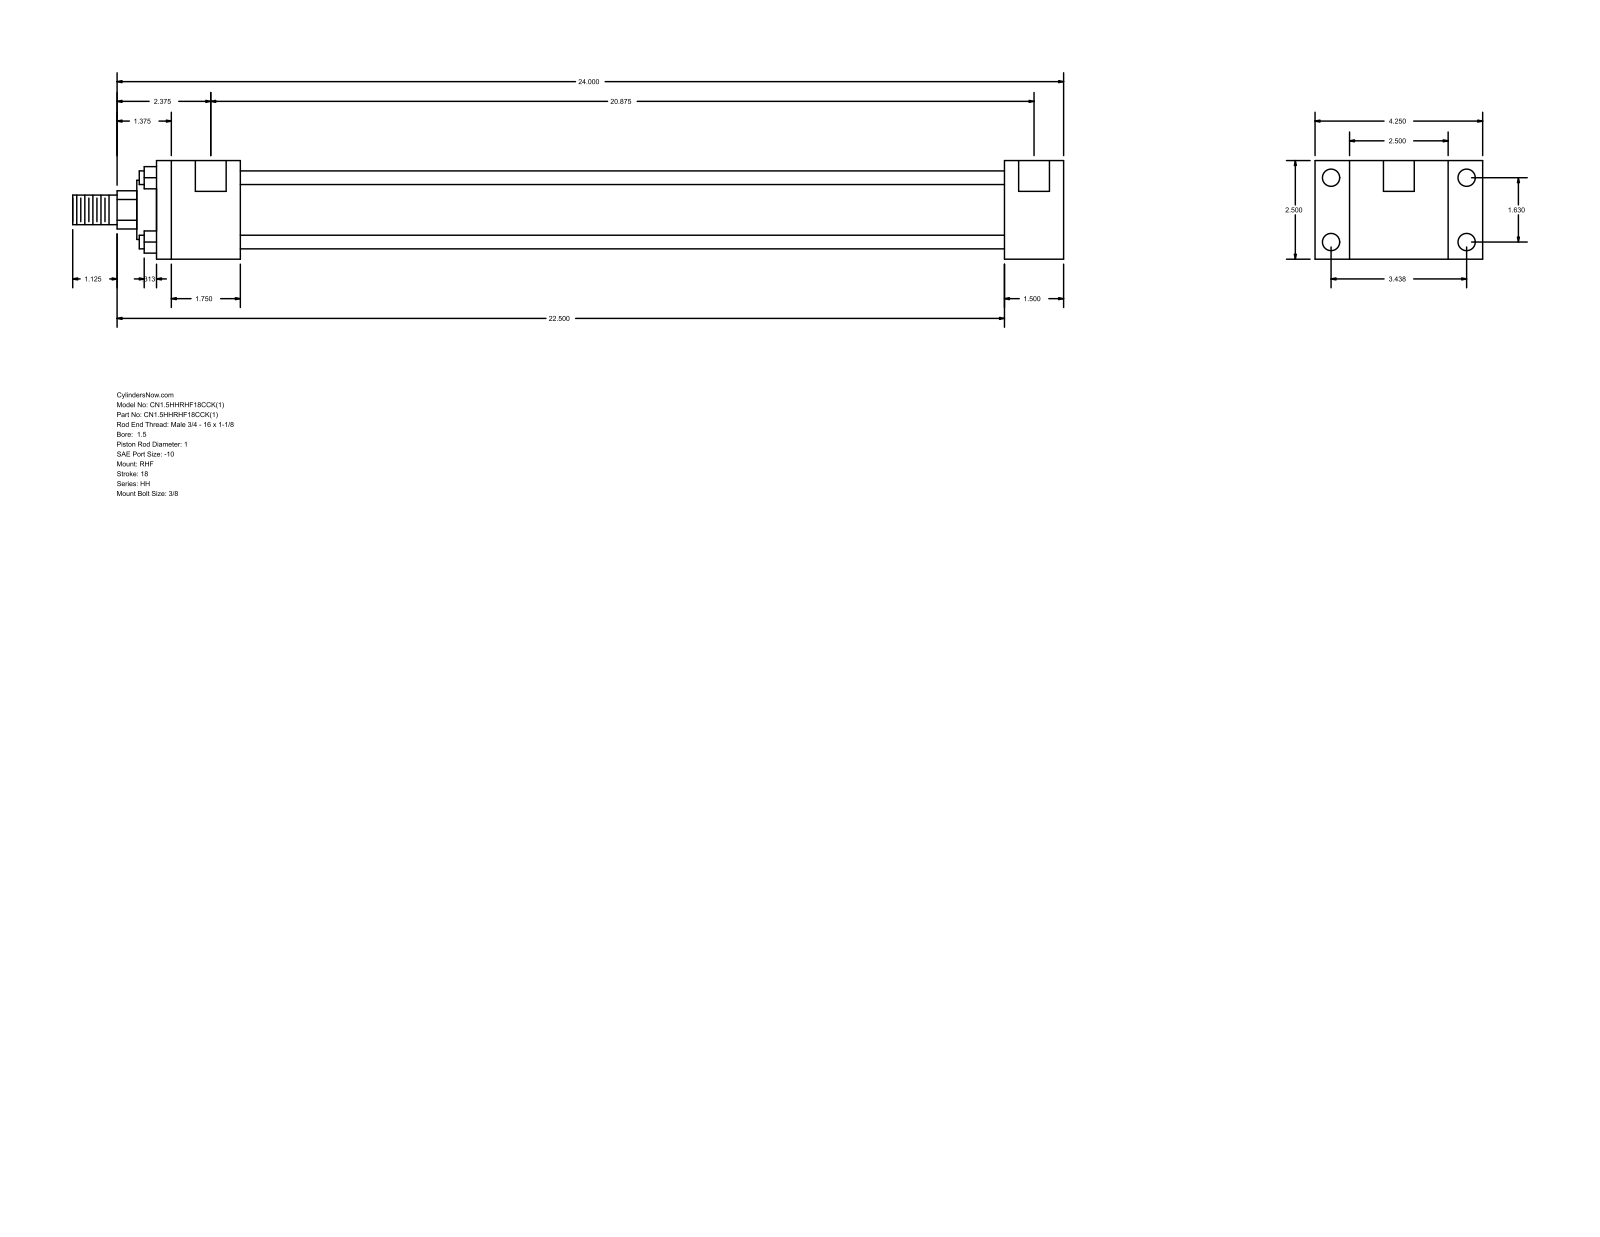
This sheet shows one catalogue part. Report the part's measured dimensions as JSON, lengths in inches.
{"part_name": "HH_RHF__0150_1", "step_written_by": "GSSL Pune (CONFIG_CONTROL_DESIGN)", "units": "inches", "bodies": {"solids": 0, "faces": 88, "planar": 60, "cylindrical": 28, "other": 0}, "overall_size": [25.125, 4.25, 2.5], "round_holes": [[0.219, 4], [0.438, 4], [0.781, 2]], "round_bosses_or_shafts": [[0.345, 4], [1.75, 1], [1.5, 1], [1, 1], [0.75, 1]], "partial_cylinders_radius": [[0.484, 1]], "face_to_face_distances": [2.5, 0.875, 3.375, 1.5, 4.25, 19.375, 20.875, 2.125, 21.5, 23], "hole_center_spacings": [0.063, 1.63, 3.438, 3.805, 20.937, 21, 20.875]}
